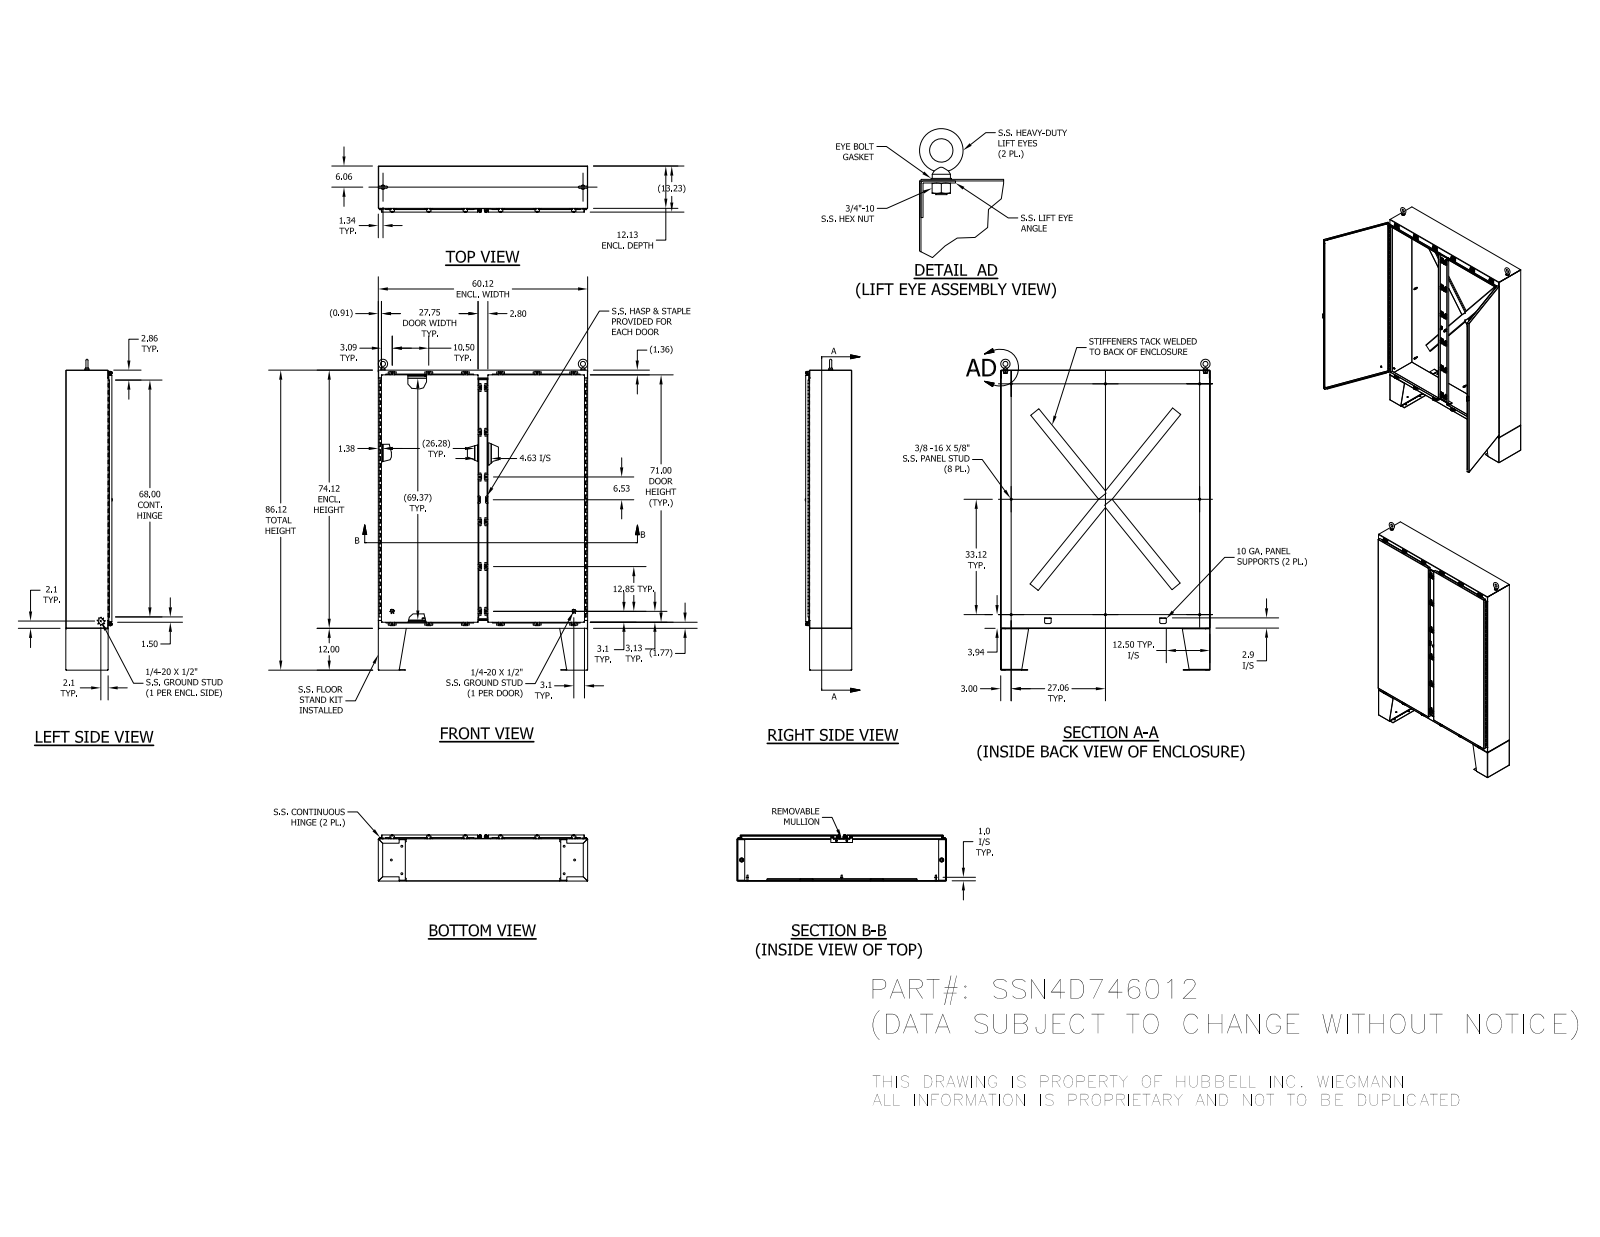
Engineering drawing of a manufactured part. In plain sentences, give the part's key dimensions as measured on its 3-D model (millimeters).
The part is named "30824-2_1; SSN4D746012; 31666_1; SSN4D6012BTM_1 (+8 more)". Its 3-D file was written by "SolidWorks 2014 (AUTOMOTIVE_DESIGN)". It is 185 solids with 6996 faces: 2802 planar, 2798 cylindrical and 1396 other. Overall it measures 2266.9 by 1527.2 by 339.2 millimeters. Its volume is 23 970 000 cubic millimeters and its surface area 19 980 000 square millimeters. Round holes: 48 of diameter 2.8, 24 of diameter 5.4, 24 of diameter 7.1, 24 of diameter 7.6, 18 of diameter 14.3, 16 of diameter 9.5, 4 of diameter 5, 4 of diameter 5.1, 4 of diameter 7.9, 4 of diameter 8, 2 of diameter 3.6, 2 of diameter 4. Round bosses or shafts: 31 of diameter 6.4, 24 of diameter 13.2, 24 of diameter 12.7, 24 of diameter 8.9, 10 of diameter 8.4, 8 of diameter 15.9, 4 of diameter 11.1, 3 of diameter 8.6. Partial cylindrical surfaces (rounded edges, fillets, slot ends): 268 of radius 0.8, 62 of radius 3.2, 48 of radius 3.6, 37 of radius 6.4, 34 of radius 1.6, 24 of radius 0.8, 24 of radius 2.5, 16 of radius 0.4. The main face-to-face distances are 2.4, 333.6, 331.2, 336, 1524.8, 305.6, 28, 1880.4, 3.2, 1527.2. The hole center spacings are 266.7, 1825.3, 1836.3, 1841.7, 1847.7, 22.3, 770, 22.3.
